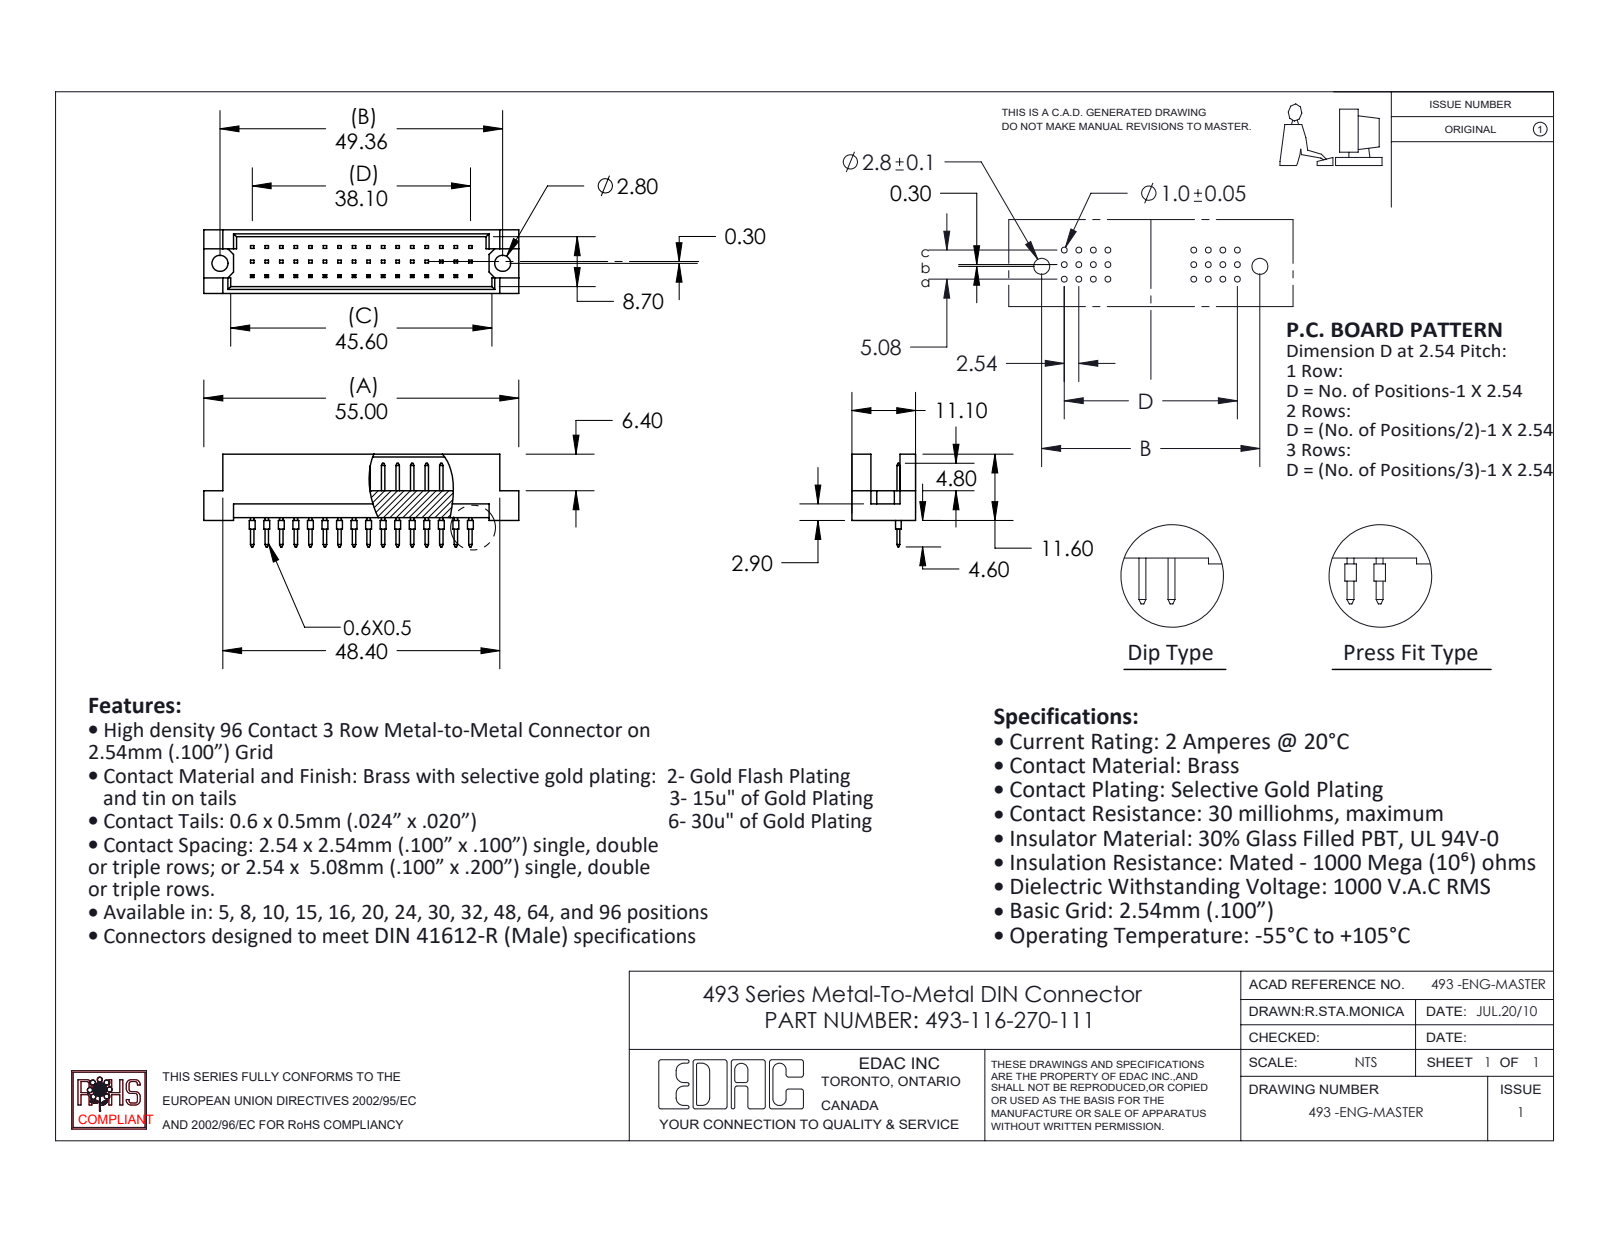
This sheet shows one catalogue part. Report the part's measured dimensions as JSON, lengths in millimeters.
{"part_name": "493-116-270-111; 493 Part_48; 493-290_70", "step_written_by": "SolidWorks 2020 (CONFIG_CONTROL_DESIGN)", "units": "millimeters", "bodies": {"solids": 17, "faces": 596, "planar": 560, "cylindrical": 36, "other": 0}, "overall_size": [55, 16.2, 11.1], "volume_mm3": 3352, "surface_area_mm2": 4302, "round_holes": [[2.8, 2]], "round_bosses_or_shafts": [[1, 16]], "face_to_face_distances": [1.2, 9.9, 11.1, 8.7, 4.7, 0.5, 2.54, 5.08, 2.76, 8.34], "hole_center_spacings": [49.36]}
